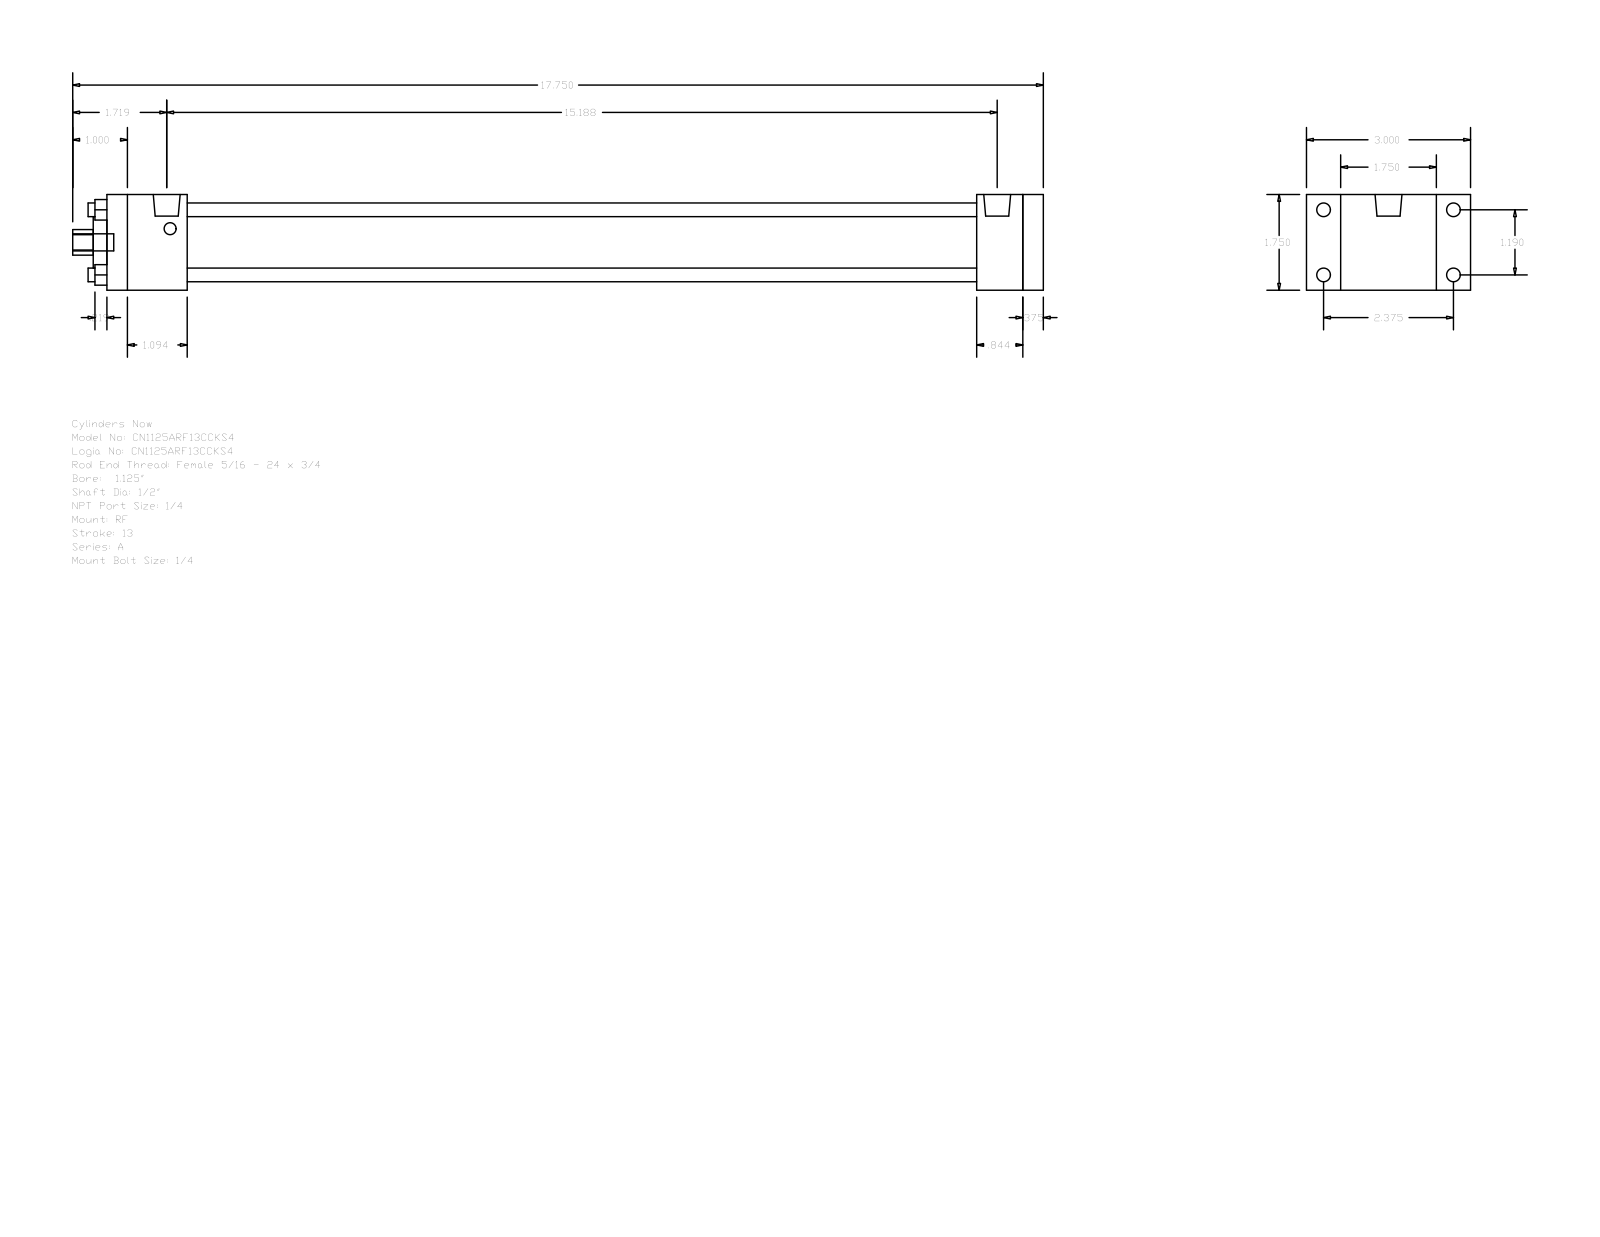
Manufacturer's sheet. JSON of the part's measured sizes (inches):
{"part_name": "A_RF__0112_0.5", "step_written_by": "GSSL Pune (CONFIG_CONTROL_DESIGN)", "units": "inches", "bodies": {"solids": 0, "faces": 92, "planar": 64, "cylindrical": 28, "other": 0}, "overall_size": [17.75, 3, 1.75], "round_holes": [[0.25, 4], [0.5, 1], [0.937, 1], [1.255, 1]], "round_bosses_or_shafts": [[0.25, 4], [0.219, 4], [0.492, 2], [0.313, 1]], "partial_cylinders_radius": [[0.234, 1]], "face_to_face_distances": [1.75, 0.375, 17.125, 16.75, 1.469, 15.906, 14.437, 15.281, 15.656, 0.844], "hole_center_spacings": [0.841, 1.19, 1.683]}
